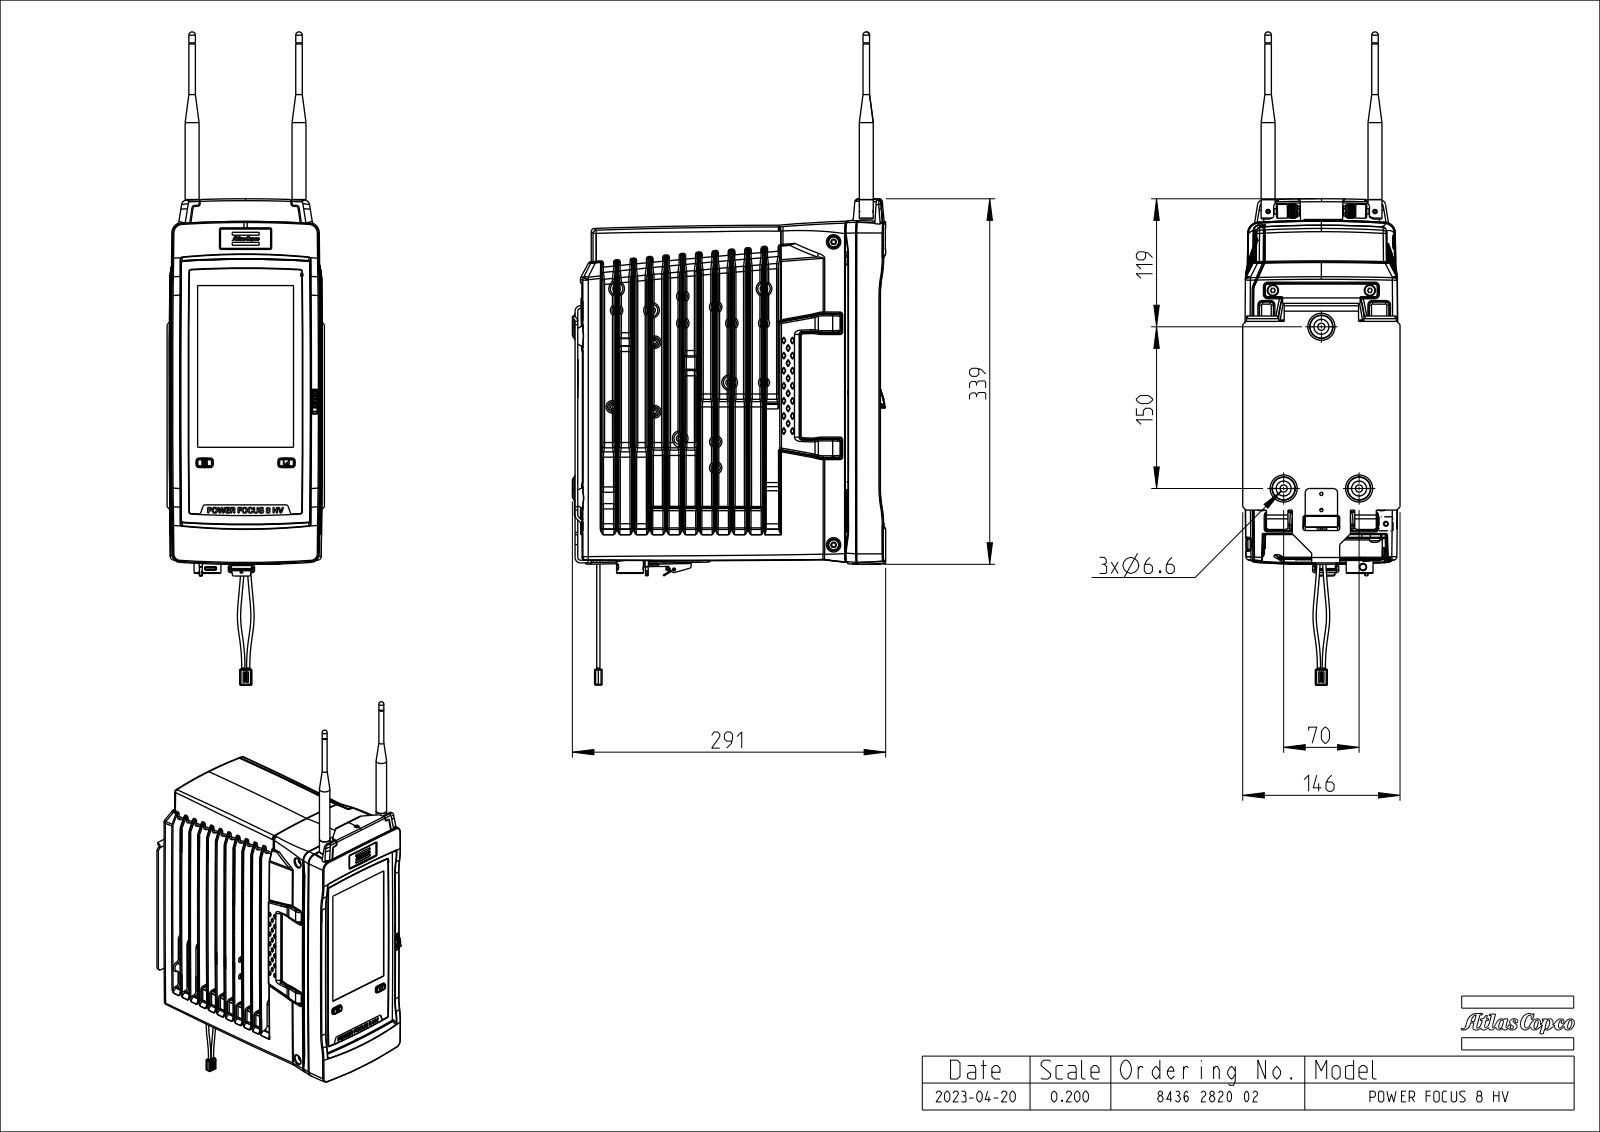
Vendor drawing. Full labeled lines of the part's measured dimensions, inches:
Part name (STEP PRODUCT): EXTTTT_COMP_SW0001
STEP written by: CREO PARAMETRIC BY PTC INC, 2022414 (AP242_MANAGED_MODEL_BASED_3D_ENGINEERING_MIM_LF)
Units: inches
Bodies: 13 solids, 23739 faces (11544 planar, 2591 cylindrical, 9604 other)
Overall size (bounding box): 22.221 × 11.427 × 5.748
Volume: 138.5 in³ · Surface area: 2 368 in²
Round holes (diameter × count): ⌀0.098 ×51, ⌀0.134 ×13, ⌀0.165 ×13, ⌀0.071 ×11, ⌀0.104 ×11, ⌀0.118 ×8, ⌀0.13 ×8, ⌀0.189 ×5, ⌀0.26 ×5, ⌀0.375 ×4, ⌀0.187 ×3, ⌀0.213 ×3
Round bosses / shafts (diameter × count): ⌀0.197 ×13, ⌀0.374 ×10, ⌀0.75 ×4, ⌀0.236 ×4, ⌀0.22 ×4, ⌀0.071 ×4, ⌀0.118 ×3, ⌀0.51 ×2
Partial cylindrical surfaces — rounded edges, fillets, slot ends (radius × count): R0.02 ×462, R0.039 ×385, R0.079 ×98, R0.007 ×72, R0.019 ×72, R0.033 ×72, R0.059 ×49, R0.118 ×41
Main face-to-face distances: 0.098, 0.787, 0.028, 10.782, 10.789, 10.881, 10.888, 0.827, 0.033, 0.079
Hole centre spacings: 4.803, 10.026, 0.315, 1.044, 0.02, 0.156, 0.157, 0.194
